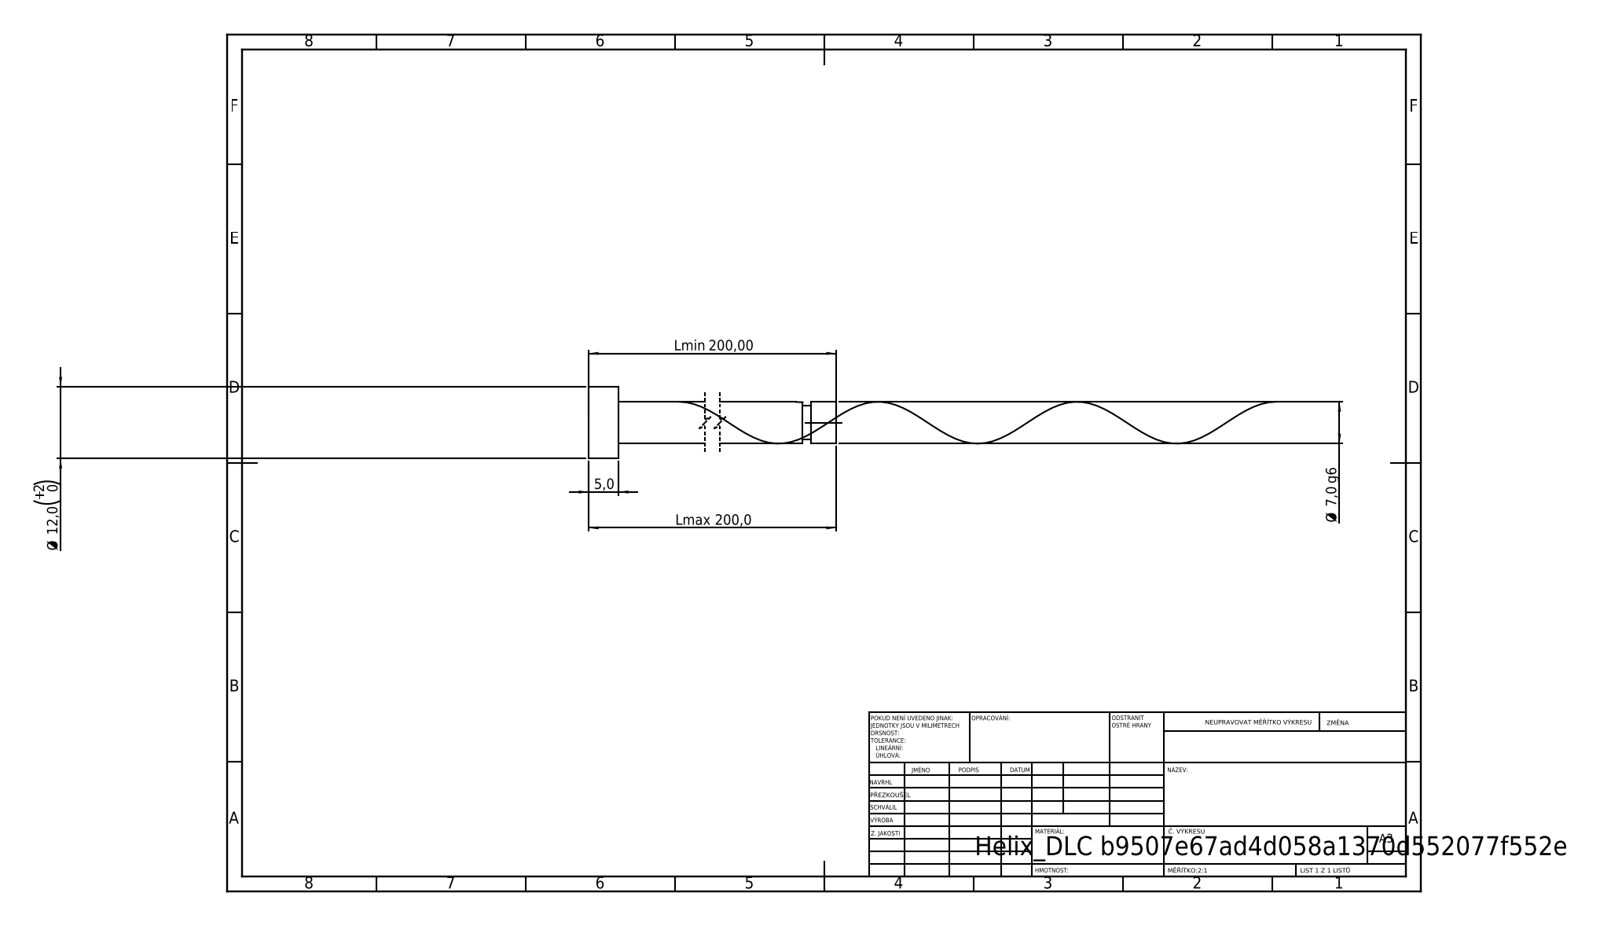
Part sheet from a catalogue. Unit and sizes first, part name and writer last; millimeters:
Units: millimetres
Overall size (bounding box): 200 × 12 × 12
Round bosses / shafts (diameter × count): ⌀12 ×1, ⌀7 ×1, ⌀5.6 ×1
Main face-to-face distances: 5, 200, 195, 195.79, 190.79, 4.21, 194.39, 189.39, 1.4, 5.61
Volume: 7 977 mm³ · Surface area: 4 810 mm²
Bodies: 1 solid, 21 faces (6 planar, 14 cylindrical, 1 other)
STEP written by: SolidWorks 2019 (CONFIG_CONTROL_DESIGN)
